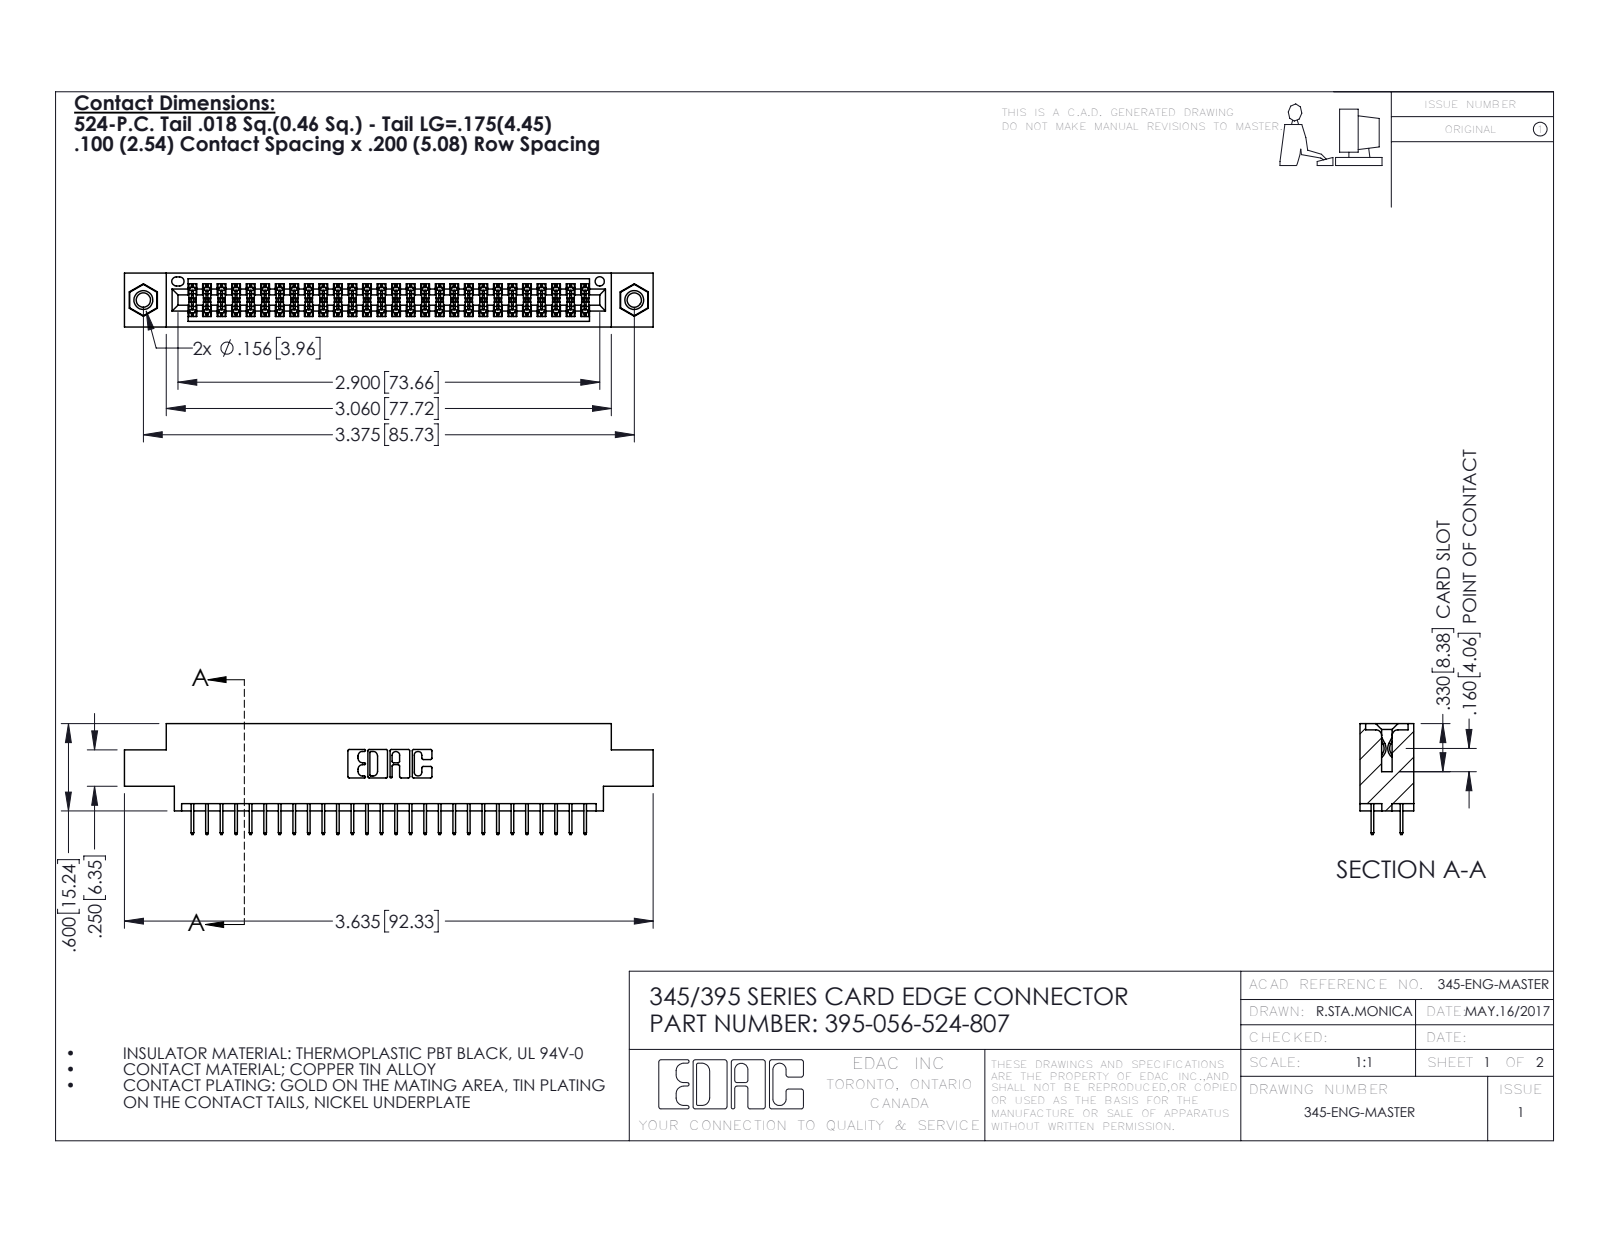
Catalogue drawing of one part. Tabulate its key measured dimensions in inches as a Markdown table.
| quantity | value |
| --- | --- |
| part name | 345-292-001_345-293-124; 395-056-524-807; 345-250-001_345-250-005-103; 345 Part_0.170 Offset - 0.156 Dia-TI |
| STEP written by | SolidWorks 2016 (CONFIG_CONTROL_DESIGN) |
| units | inches |
| bodies | 59 solids, 3214 faces (2300 planar, 898 cylindrical, 16 other) |
| overall size | 3.635 × 0.762 × 0.37 |
| volume | 0.526 in³ |
| surface area | 19.27 in² |
| round holes (diameter × count) | 0.098 × 2, 0.125 × 2, 0.156 × 2, 0.064 × 1 |
| round bosses / shafts (diameter × count) | 0.155 × 2 |
| partial cylindrical surfaces (radius × count) | 0.006 × 84, 0.01 × 22, 0.007 × 6, 0.031 × 6, 0.026 × 3, 0.014 × 2, 0.019 × 2, 0.022 × 2 |
| main face-to-face distances | 0.072, 0.298, 0.37, 0.2, 0.098, 0.272, 0.025, 0.225, 0.175, 0.072 |
| hole center spacings | 0.27, 3.14, 3.375 |
